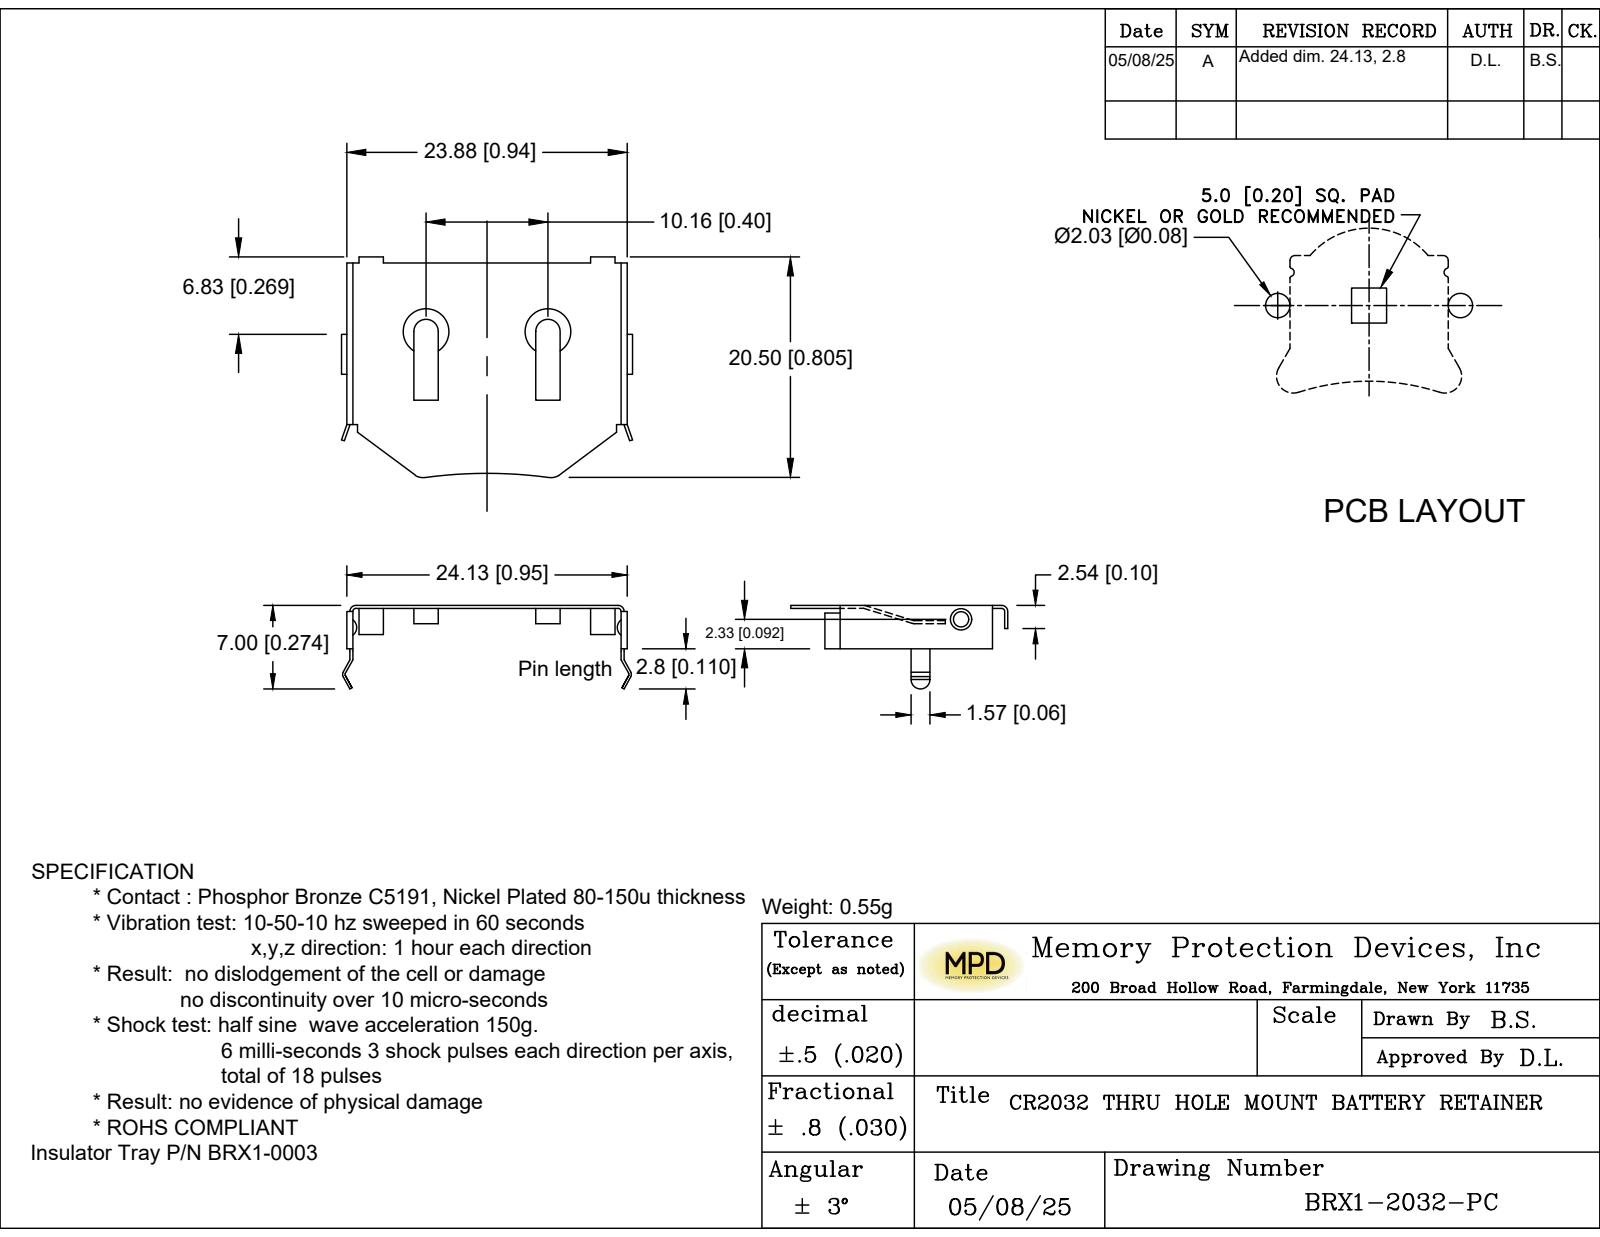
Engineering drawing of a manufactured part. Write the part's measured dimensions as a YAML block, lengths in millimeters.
part_name: "BRX1-2032-PC"
step_written_by: "SolidWorks 2017 (AUTOMOTIVE_DESIGN)"
units: millimeters
bodies: {solids: 1, faces: 180, planar: 111, cylindrical: 53, other: 16}
overall_size: [25.04, 20.5, 6.96]
volume: 130
surface_area: 1179
round_holes:
  - {diameter: 4, count: 2}
  - {diameter: 1.19, count: 1}
round_bosses_or_shafts:
  - {diameter: 1.65, count: 1}
partial_cylinders:
  - {radius: 0.25, count: 3}
  - {radius: 0.48, count: 3}
  - {radius: 0.17, count: 2}
  - {radius: 0.3, count: 2}
  - {radius: 0.4, count: 2}
  - {radius: 0.5, count: 2}
  - {radius: 0.53, count: 2}
  - {radius: 0.73, count: 2}
face_to_face_distances: [23.65, 23.88, 23.42, 1.83, 2.06, 1.6, 2.1, 2.33, 3.93, 4.16]
hole_center_spacings: [10.16]
